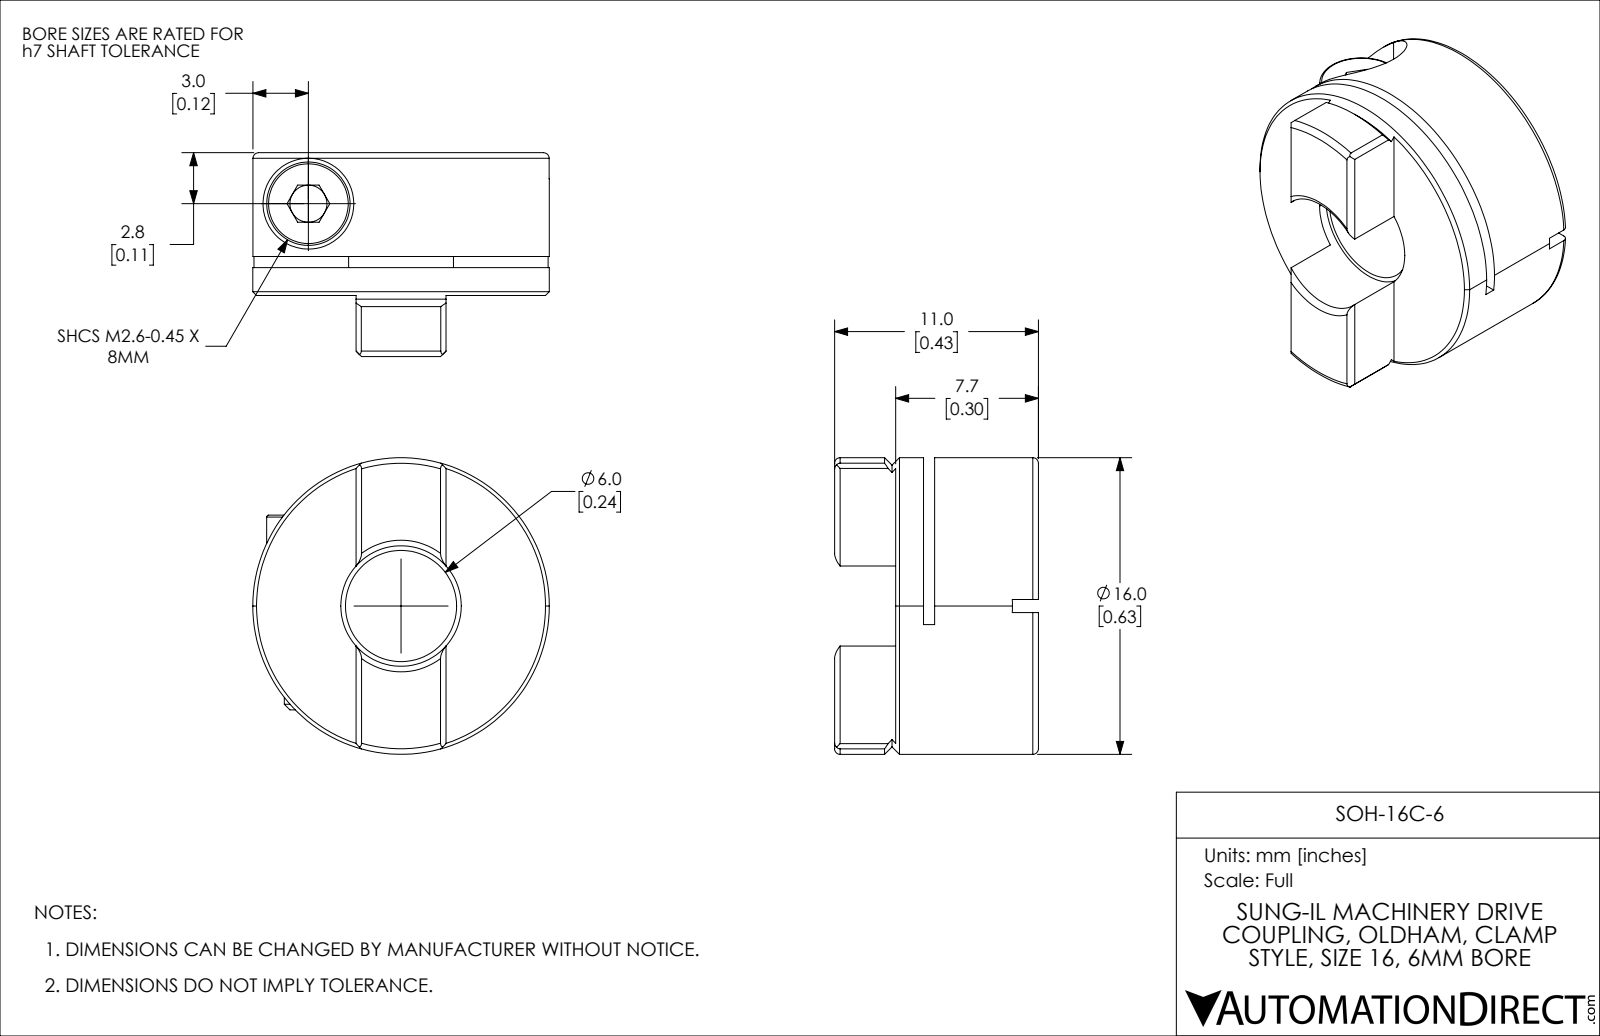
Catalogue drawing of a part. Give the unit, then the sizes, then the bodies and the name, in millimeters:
Units: millimetres
Overall size (bounding box): 16 × 16 × 11
Round holes (diameter × count): ⌀2 ×1, ⌀2.05 ×1, ⌀2.8 ×1, ⌀4.9 ×1, ⌀6 ×1, ⌀6.5 ×1
Round bosses / shafts (diameter × count): ⌀16 ×1, ⌀4.5 ×1, ⌀2.6 ×1
Partial cylindrical surfaces — rounded edges, fillets, slot ends (radius × count): R22.5 ×1
Main face-to-face distances: 7.7, 6.2, 1.5, 5.6, 0.6, 2.1, 4.8, 0.7, 11, 5.4
Volume: 1 367 mm³ · Surface area: 1 466 mm²
Bodies: 2 solids, 93 faces (44 planar, 25 cylindrical, 24 other)
Part name (STEP PRODUCT): SOH-16C-6
STEP written by: SolidWorks 2021 (CONFIG_CONTROL_DESIGN)
